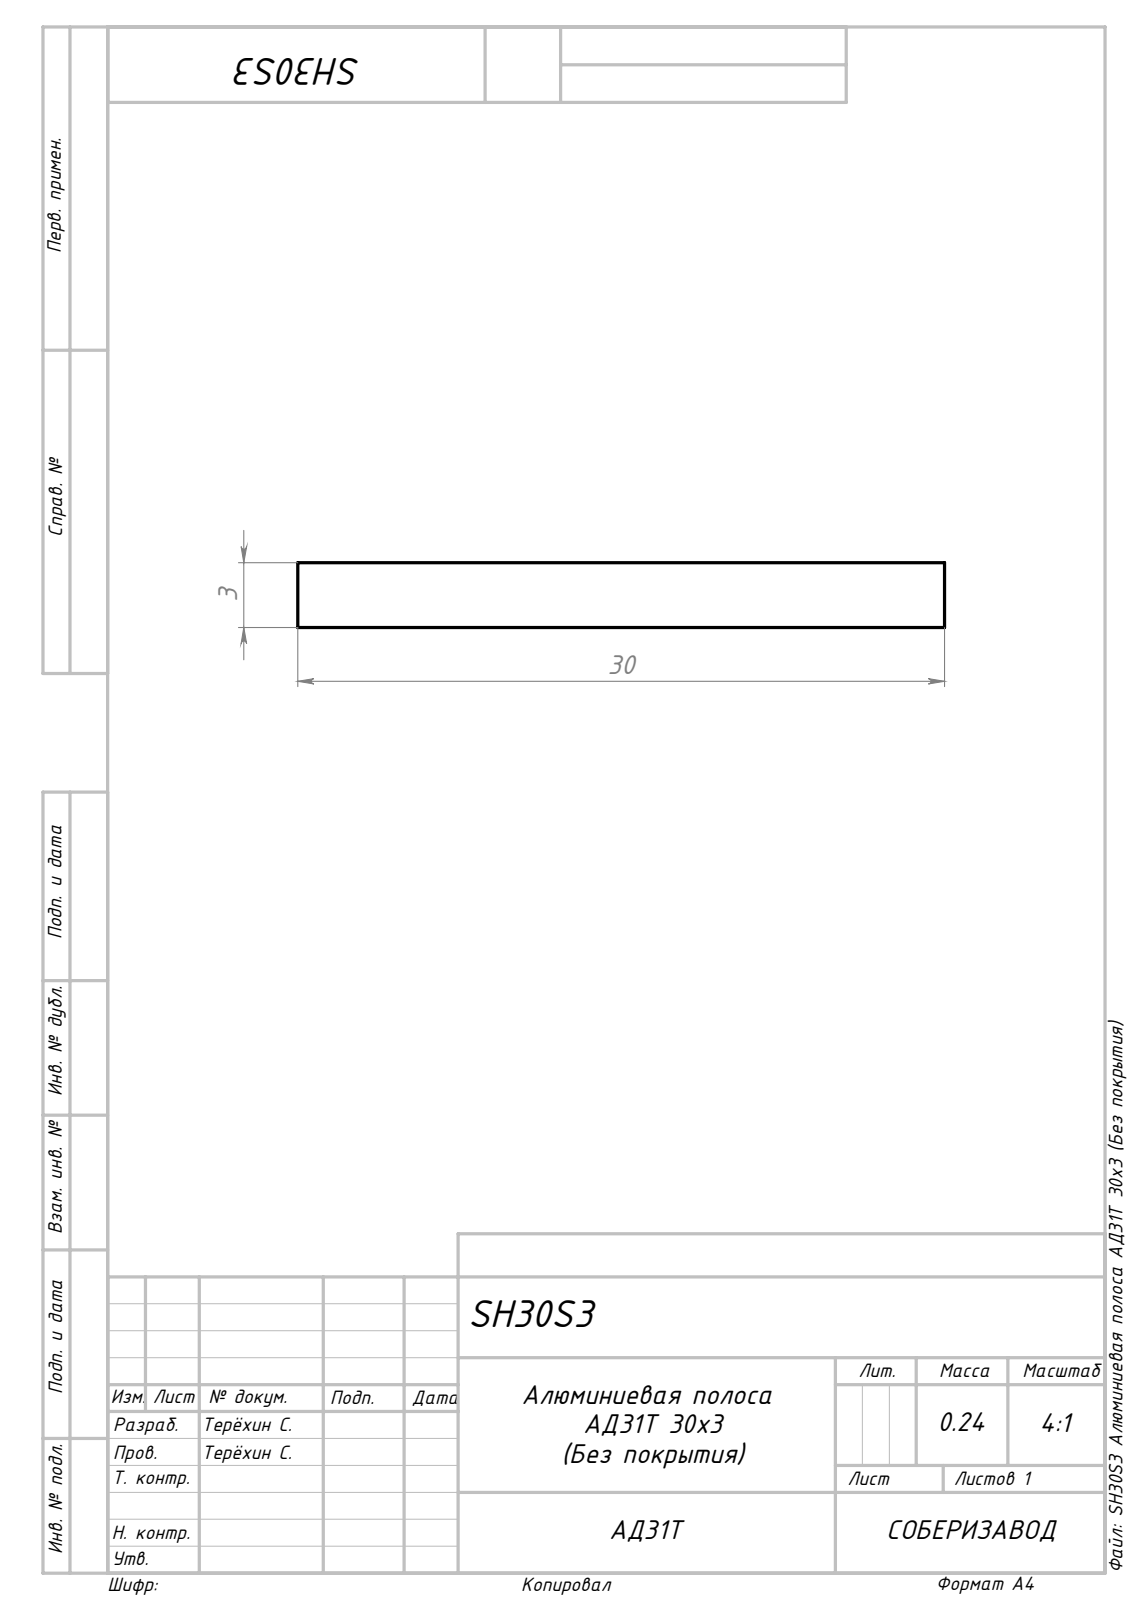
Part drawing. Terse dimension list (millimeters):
name: Сборка1; SH30S3 Алюминиевая полоса АД31Т 30х3 (Без покрытия)_30х3
written by: SolidWorks 2024 (AUTOMOTIVE_DESIGN)
unit: mm
bodies: 1 solid, 6 faces (6 planar, 0 cylindrical, 0 other)
size: 1000 × 30 × 3
volume: 90 000 mm³; area: 66 180 mm²
face distances: 3, 30, 1000
